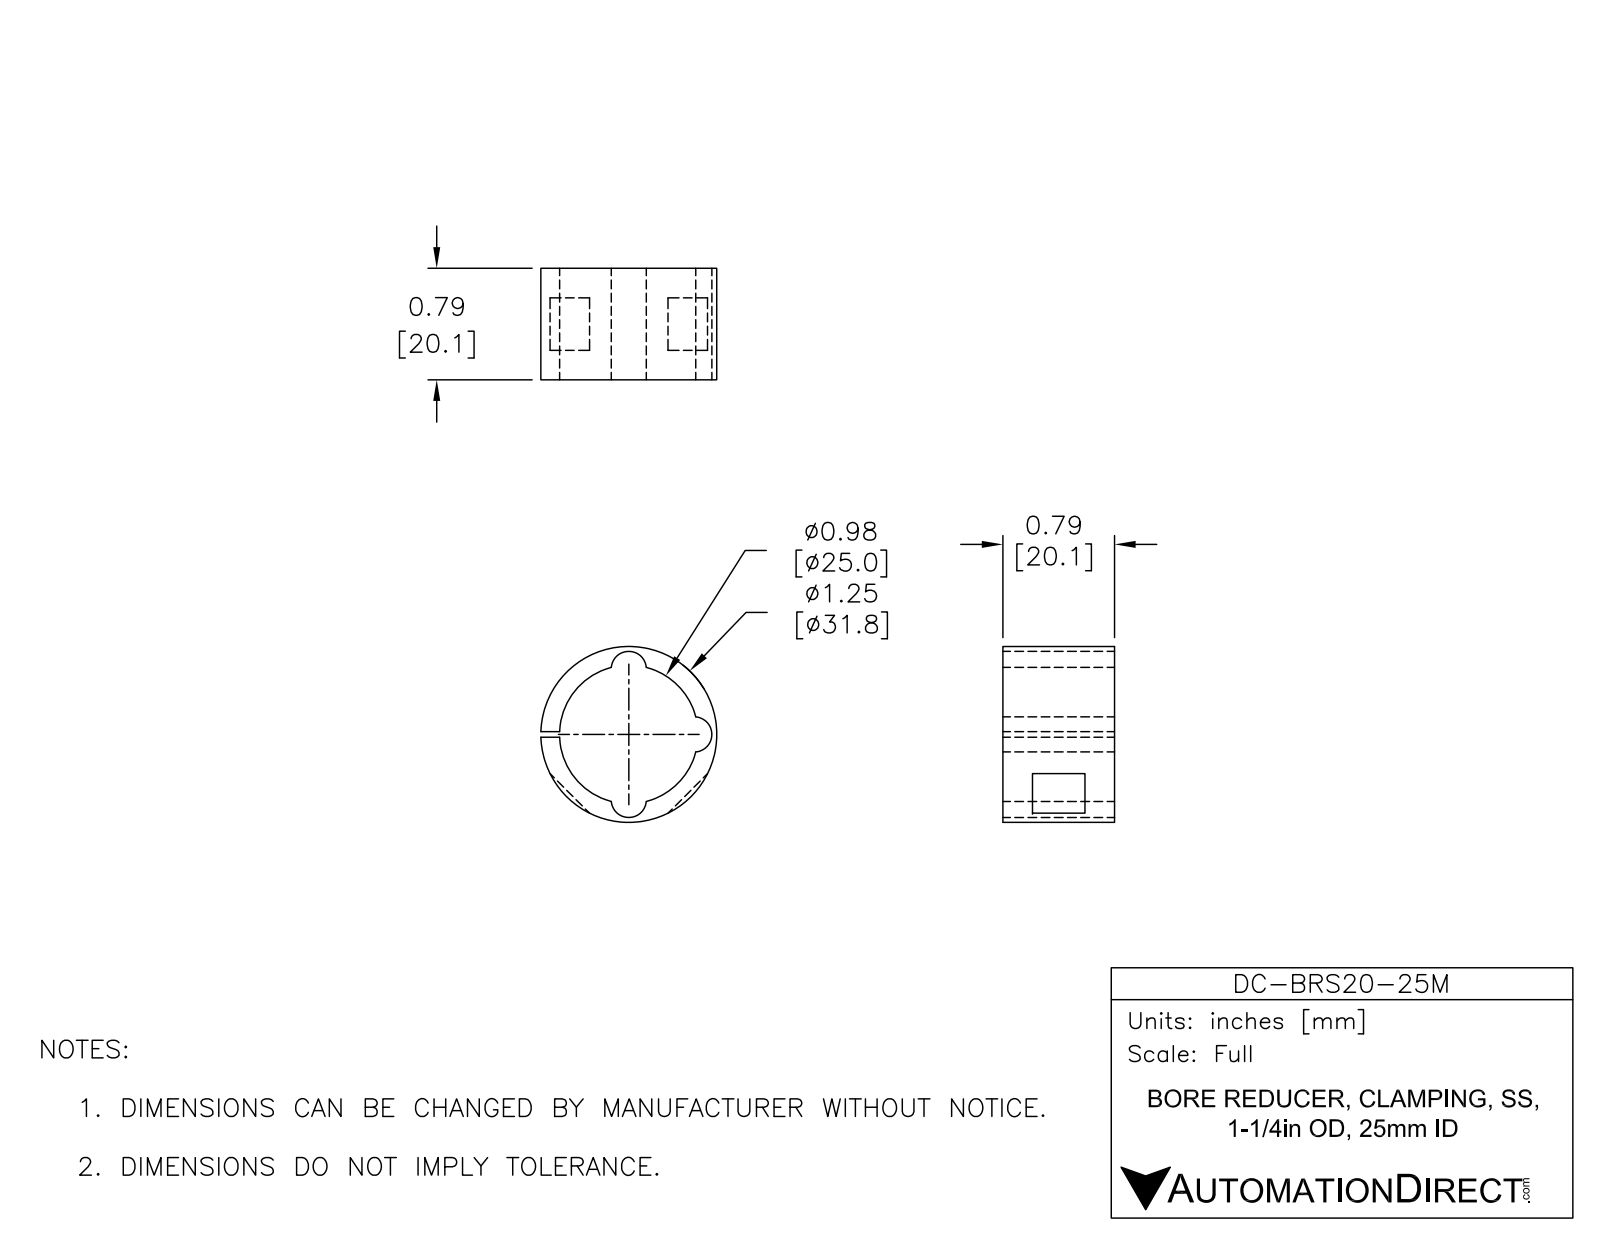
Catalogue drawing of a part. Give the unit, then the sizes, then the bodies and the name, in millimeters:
Units: millimetres
Overall size (bounding box): 31.75 × 31.74 × 20.14
Round bosses / shafts (diameter × count): ⌀31.75 ×1
Partial cylindrical surfaces — rounded edges, fillets, slot ends (radius × count): R3.17 ×3, R12.7 ×1
Main face-to-face distances: 20.14, 1.02, 5.33, 14.81, 9.48
Volume: 4 903 mm³ · Surface area: 4 379 mm²
Bodies: 1 solid, 20 faces (10 planar, 10 cylindrical, 0 other)
Part name (STEP PRODUCT): DC-BRS20-25M
STEP written by: SolidWorks 2015 (AUTOMOTIVE_DESIGN)
